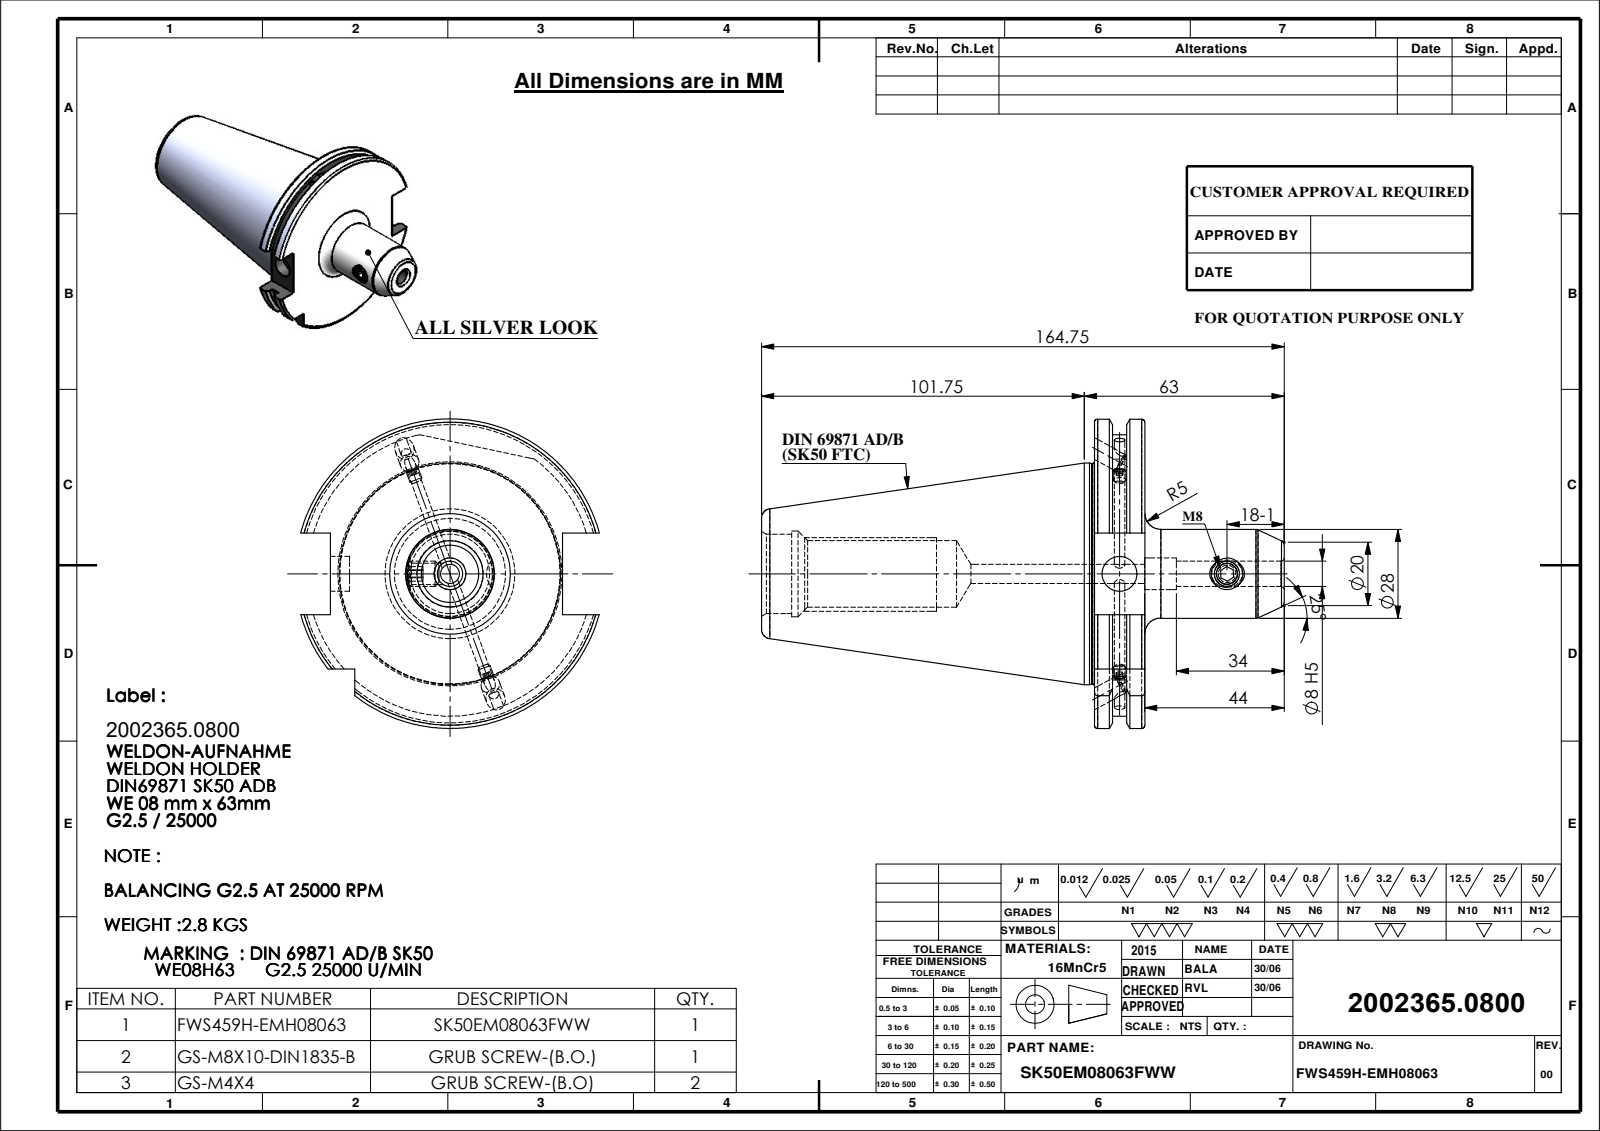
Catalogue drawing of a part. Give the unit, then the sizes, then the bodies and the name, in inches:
Units: inches
Overall size (bounding box): 6.486 × 3.839 × 3.703
Round holes (diameter × count): ⌀0.236 ×3, ⌀0.394 ×2, ⌀0.13 ×1, ⌀0.268 ×1, ⌀0.315 ×1, ⌀0.433 ×1, ⌀0.827 ×1, ⌀0.984 ×1, ⌀1.063 ×1
Round bosses / shafts (diameter × count): ⌀0.157 ×2, ⌀2.75 ×1, ⌀2.734 ×1, ⌀1.102 ×1, ⌀0.315 ×1
Partial cylindrical surfaces — rounded edges, fillets, slot ends (radius × count): R1.768 ×1, R1.919 ×1
Main face-to-face distances: 0.626, 0.223, 0.403, 0.4, 0.177, 0.226, 4.132, 4.355, 4.531, 4.758
Hole centre spacings: 1.335
Volume: 21.94 in³ · Surface area: 74.45 in²
Bodies: 4 solids, 168 faces (53 planar, 55 cylindrical, 60 other)
Part name (STEP PRODUCT): Copy of M4X4_DIN 913 - M4 x 4-N; M8X10._DIN 913 - M8 x 8-N; SK50EM08063FTCWW; 91506-WE70806.3
STEP written by: SolidWorks 2009 (CONFIG_CONTROL_DESIGN)
